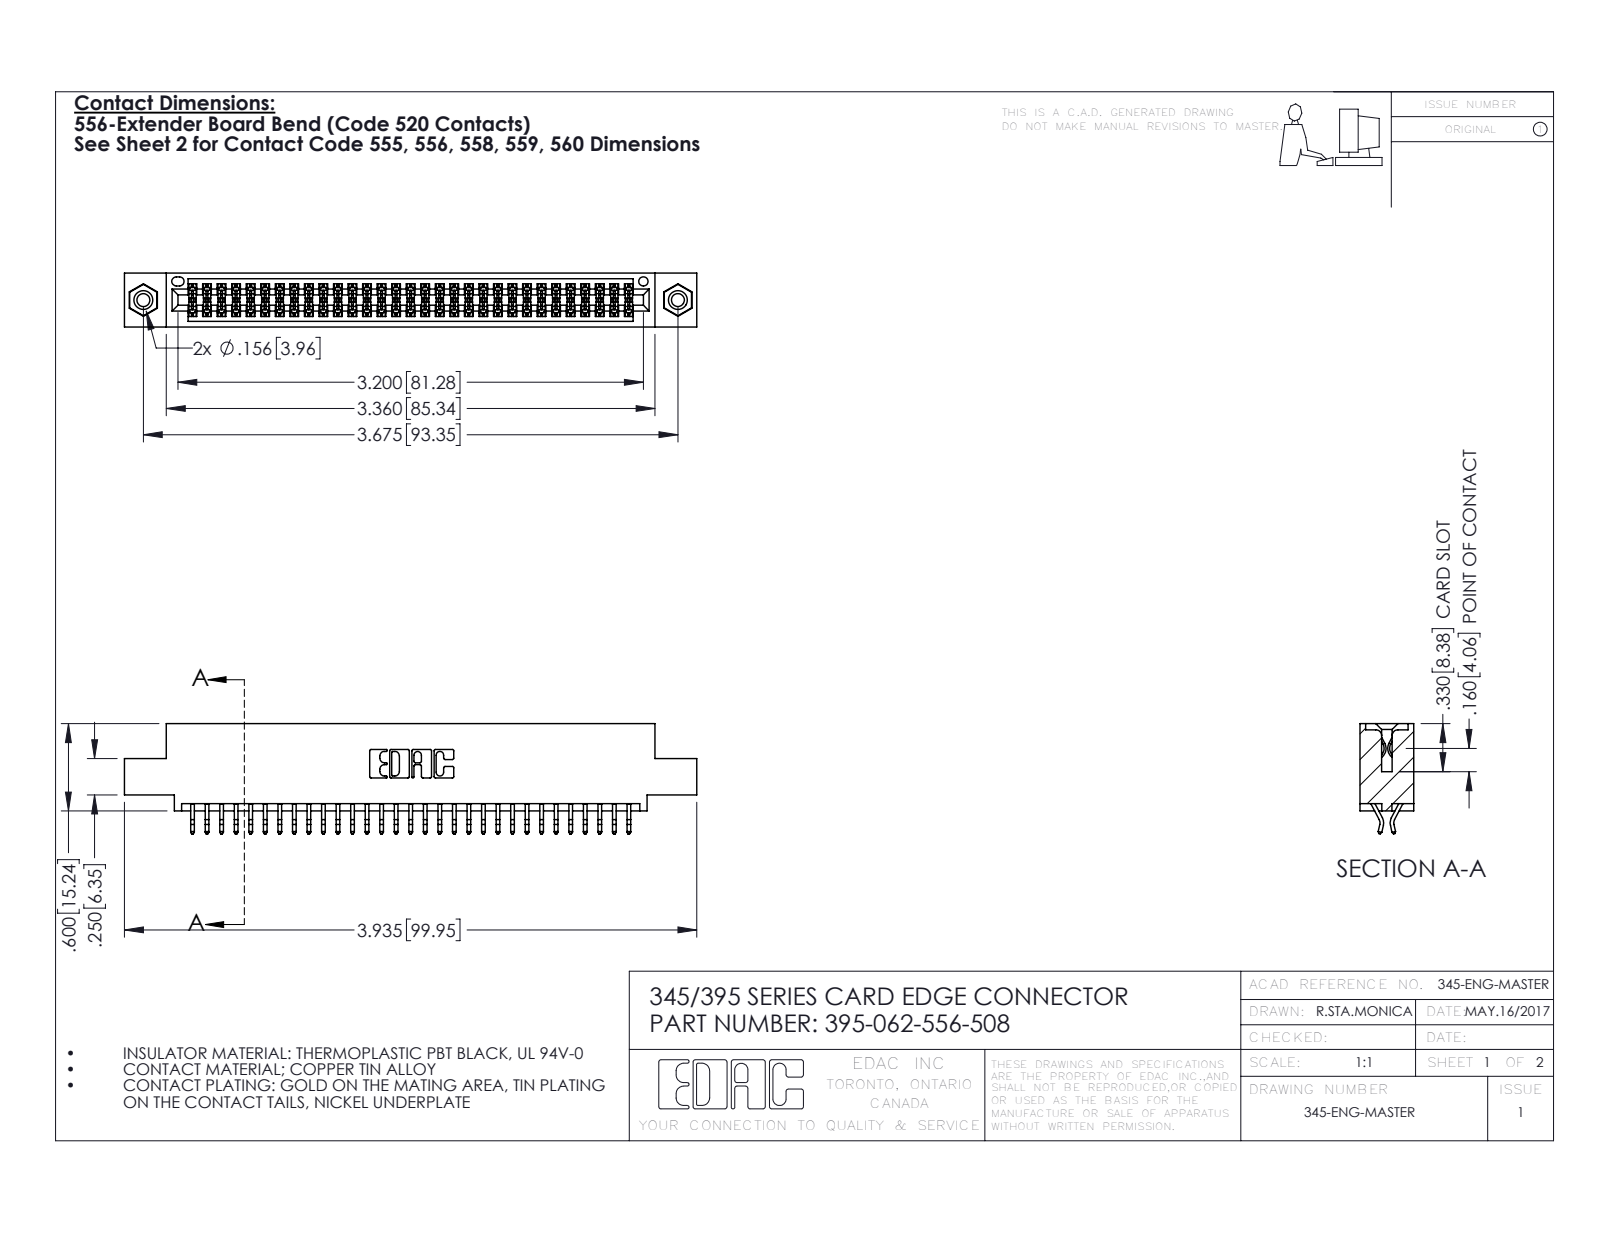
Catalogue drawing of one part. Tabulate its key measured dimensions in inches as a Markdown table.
| quantity | value |
| --- | --- |
| part name | 345 Part_0.110 Offset - 0.156 Dia-TI; 345-292-001_556 Tail; 395-062-556-508; 345-250-001_345-250-003-102 |
| STEP written by | SolidWorks 2016 (CONFIG_CONTROL_DESIGN) |
| units | inches |
| bodies | 65 solids, 3662 faces (2410 planar, 1236 cylindrical, 16 other) |
| overall size | 3.935 × 0.757 × 0.37 |
| volume | 0.581 in³ |
| surface area | 21.57 in² |
| round holes (diameter × count) | 0.089 × 2, 0.125 × 2, 0.156 × 2, 0.064 × 1 |
| round bosses / shafts (diameter × count) | 0.155 × 2 |
| partial cylindrical surfaces (radius × count) | 0.006 × 93, 0.01 × 22, 0.007 × 6, 0.031 × 6, 0.026 × 3, 0.01 × 2, 0.014 × 2, 0.019 × 2 |
| main face-to-face distances | 0.072, 0.298, 0.2, 0.37, 0.025, 0.098, 0.272, 0.225, 0.175, 0.149 |
| hole center spacings | 0.27, 3.44, 3.675 |
